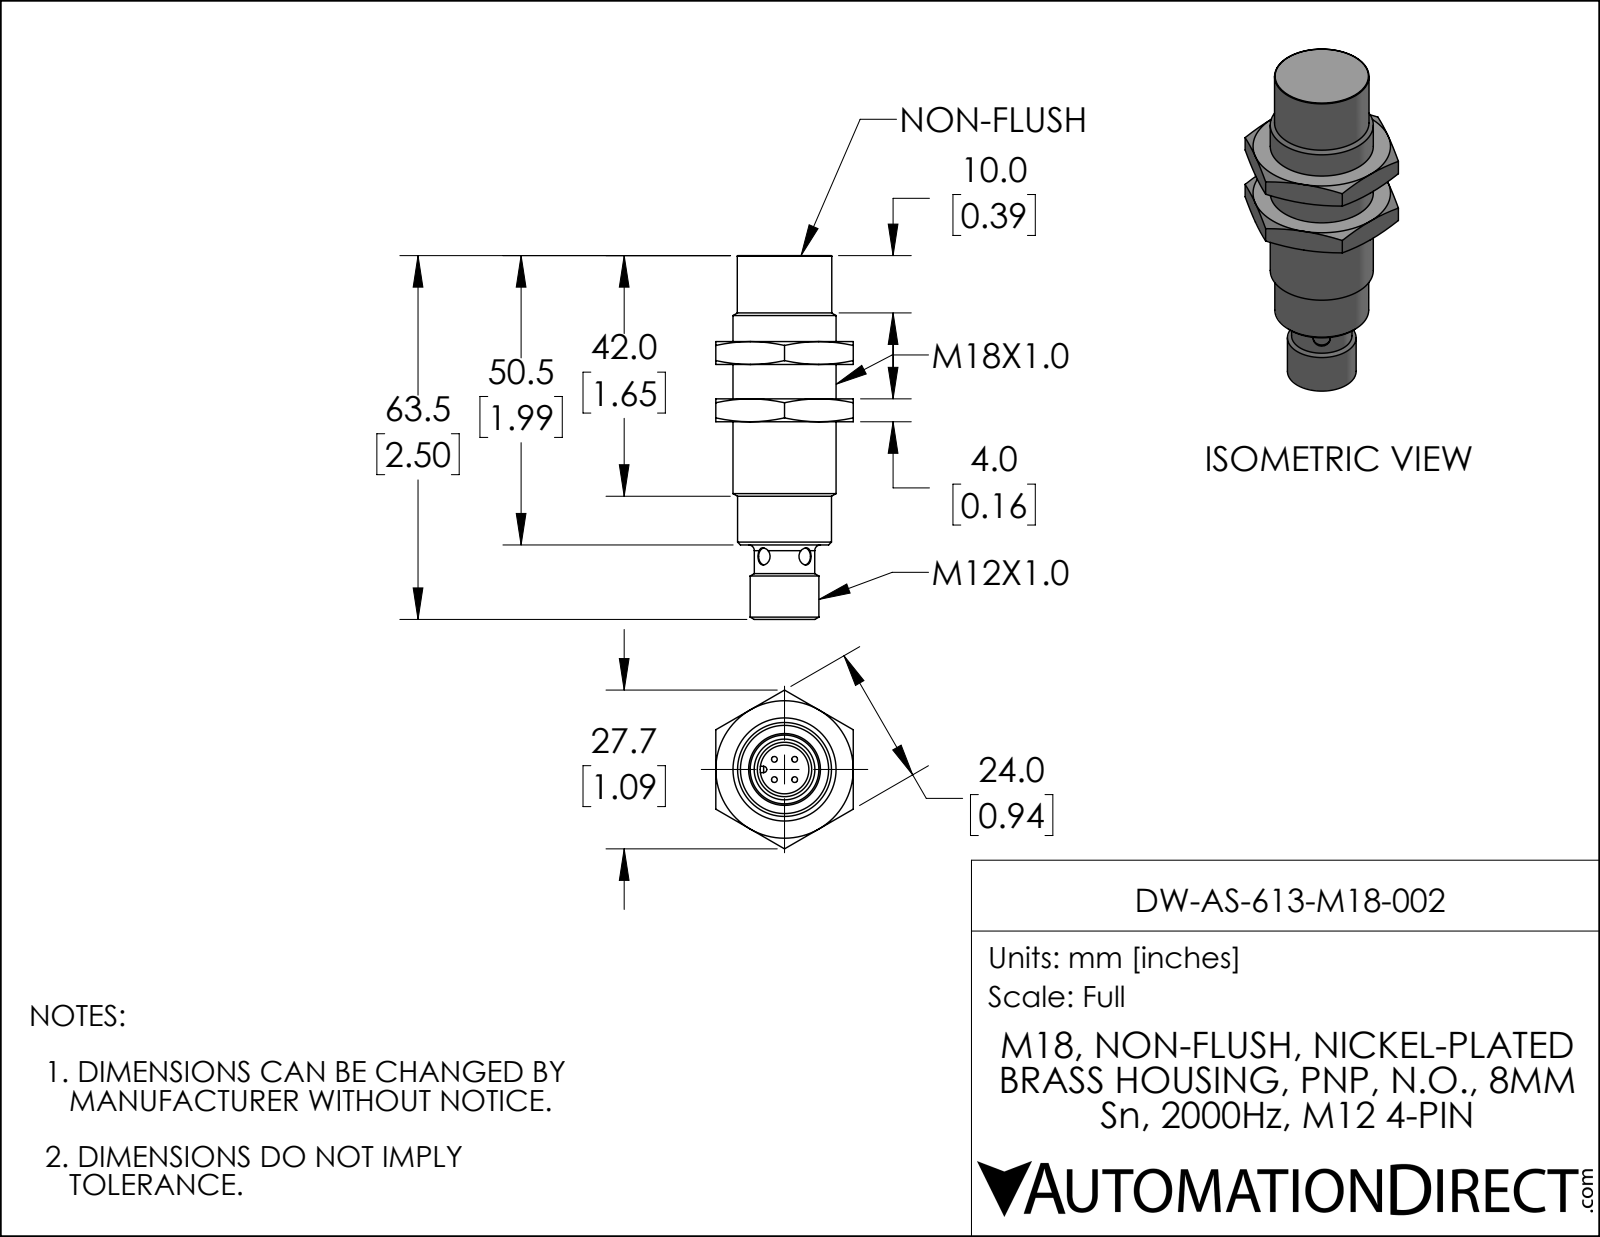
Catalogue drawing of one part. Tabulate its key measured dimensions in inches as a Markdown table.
| quantity | value |
| --- | --- |
| part name | DW-AS-613-M18-002 |
| STEP written by | SolidWorks 2019 (AUTOMOTIVE_DESIGN) |
| units | inches |
| bodies | 1 solid, 82 faces (27 planar, 18 cylindrical, 37 other) |
| overall size | 2.5 × 1.091 × 0.945 |
| volume | 0.905 in³ |
| surface area | 8.005 in² |
| round holes (diameter × count) | 0.118 × 2, 0.335 × 1 |
| round bosses / shafts (diameter × count) | 0.039 × 4, 0.709 × 1, 0.65 × 1, 0.646 × 1, 0.472 × 1, 0.415 × 1 |
| partial cylindrical surfaces (radius × count) | 0.022 × 2 |
| main face-to-face distances | 0.394, 0.157, 0.945, 0.591, 0.748, 0.984, 1.142, 0.551, 0.236, 1.988 |
